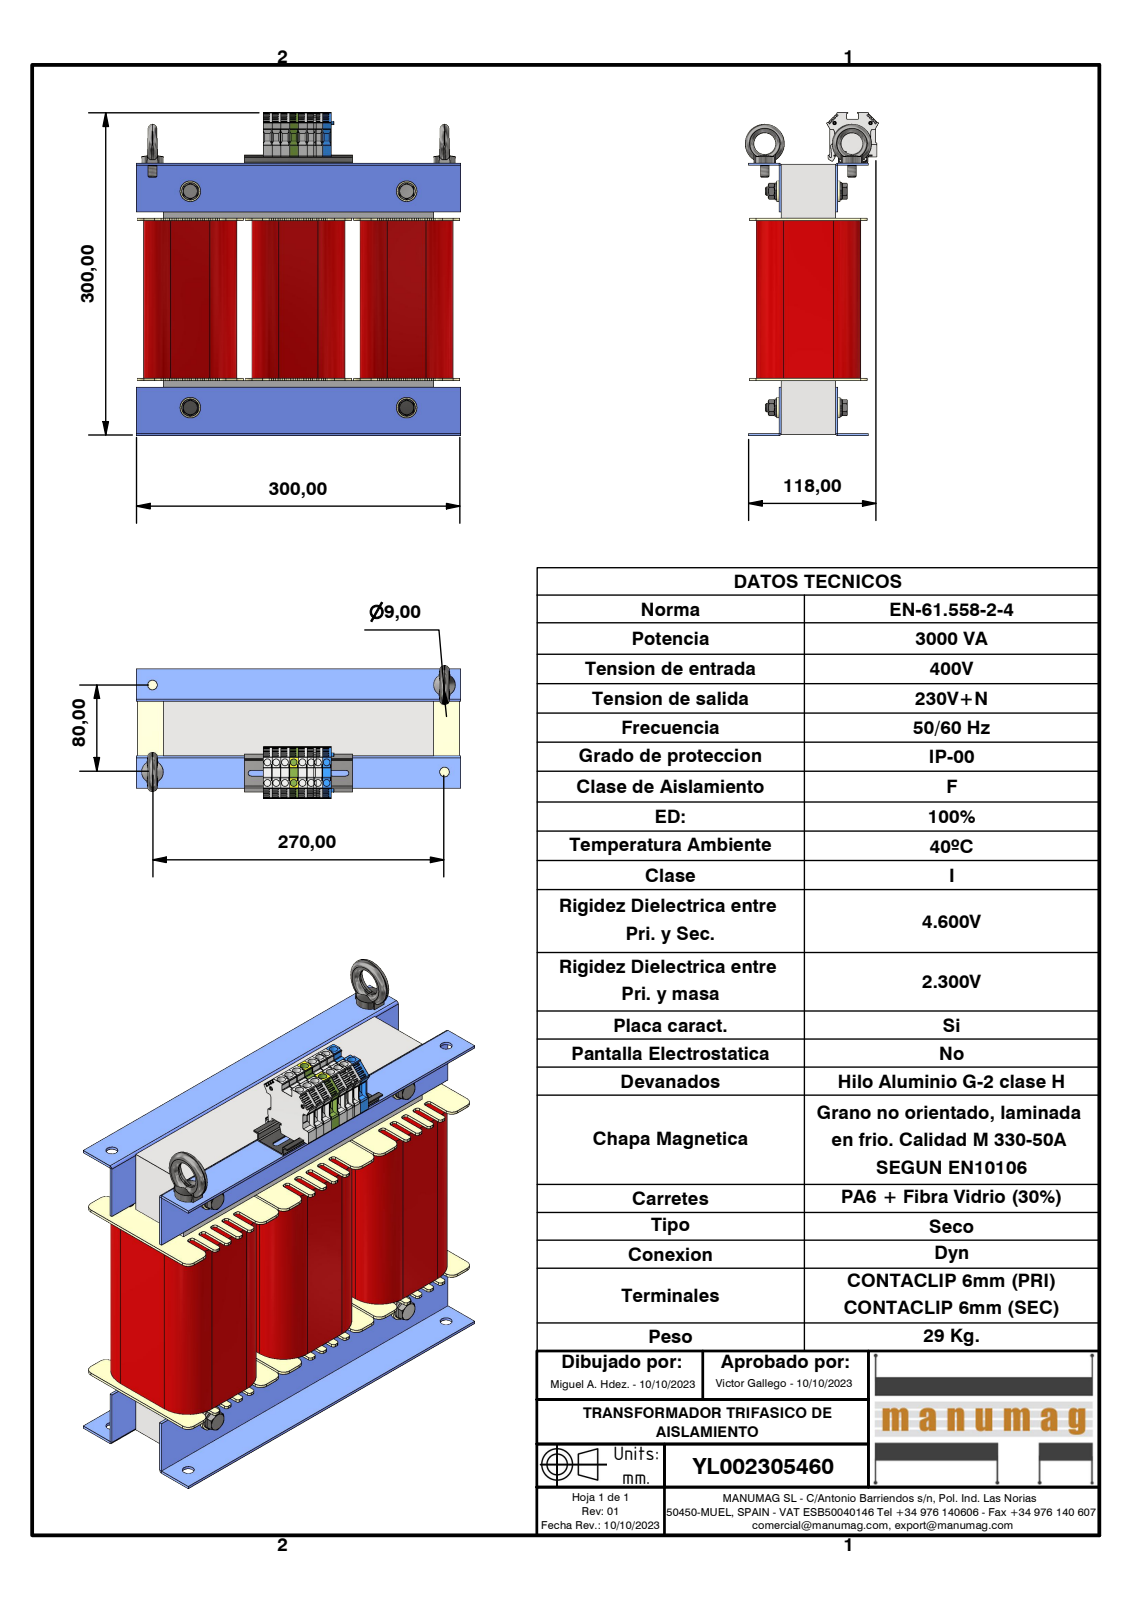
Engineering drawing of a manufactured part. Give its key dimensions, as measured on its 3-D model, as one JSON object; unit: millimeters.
{"part_name": "YL002305460; 3UI150 250 x 250 - 50 (Rc50); UI 150_50; RC50 NT050 (+8 more)", "step_written_by": "Autodesk Inventor 2023 (AUTOMOTIVE_DESIGN)", "units": "millimeters", "bodies": {"solids": 43, "faces": 3074, "planar": 2108, "cylindrical": 782, "other": 184}, "overall_size": [300, 299.05, 122.6], "volume_mm3": 5026000, "surface_area_mm2": 760988, "round_holes": [[6.3, 16], [11, 6], [6.65, 4], [8, 4], [8.4, 4], [9, 4], [10.5, 4], [2.4, 2], [2.5, 2], [2.75, 2], [2.95, 2], [20, 2]], "round_bosses_or_shafts": [[19, 4], [16, 4], [11.4, 4], [9.6, 4], [7.32, 4], [36, 2], [8, 2], [7, 2]], "partial_cylinders_radius": [[2, 109], [6, 24], [0.25, 16], [1, 15], [25, 12], [2.6, 8], [0.3, 5], [0.5, 5]], "face_to_face_distances": [50, 2, 100, 52, 200, 150, 250, 51, 1, 199], "hole_center_spacings": [8.1, 20.65, 16.2, 19, 24.97, 24.3, 30.85, 200]}
